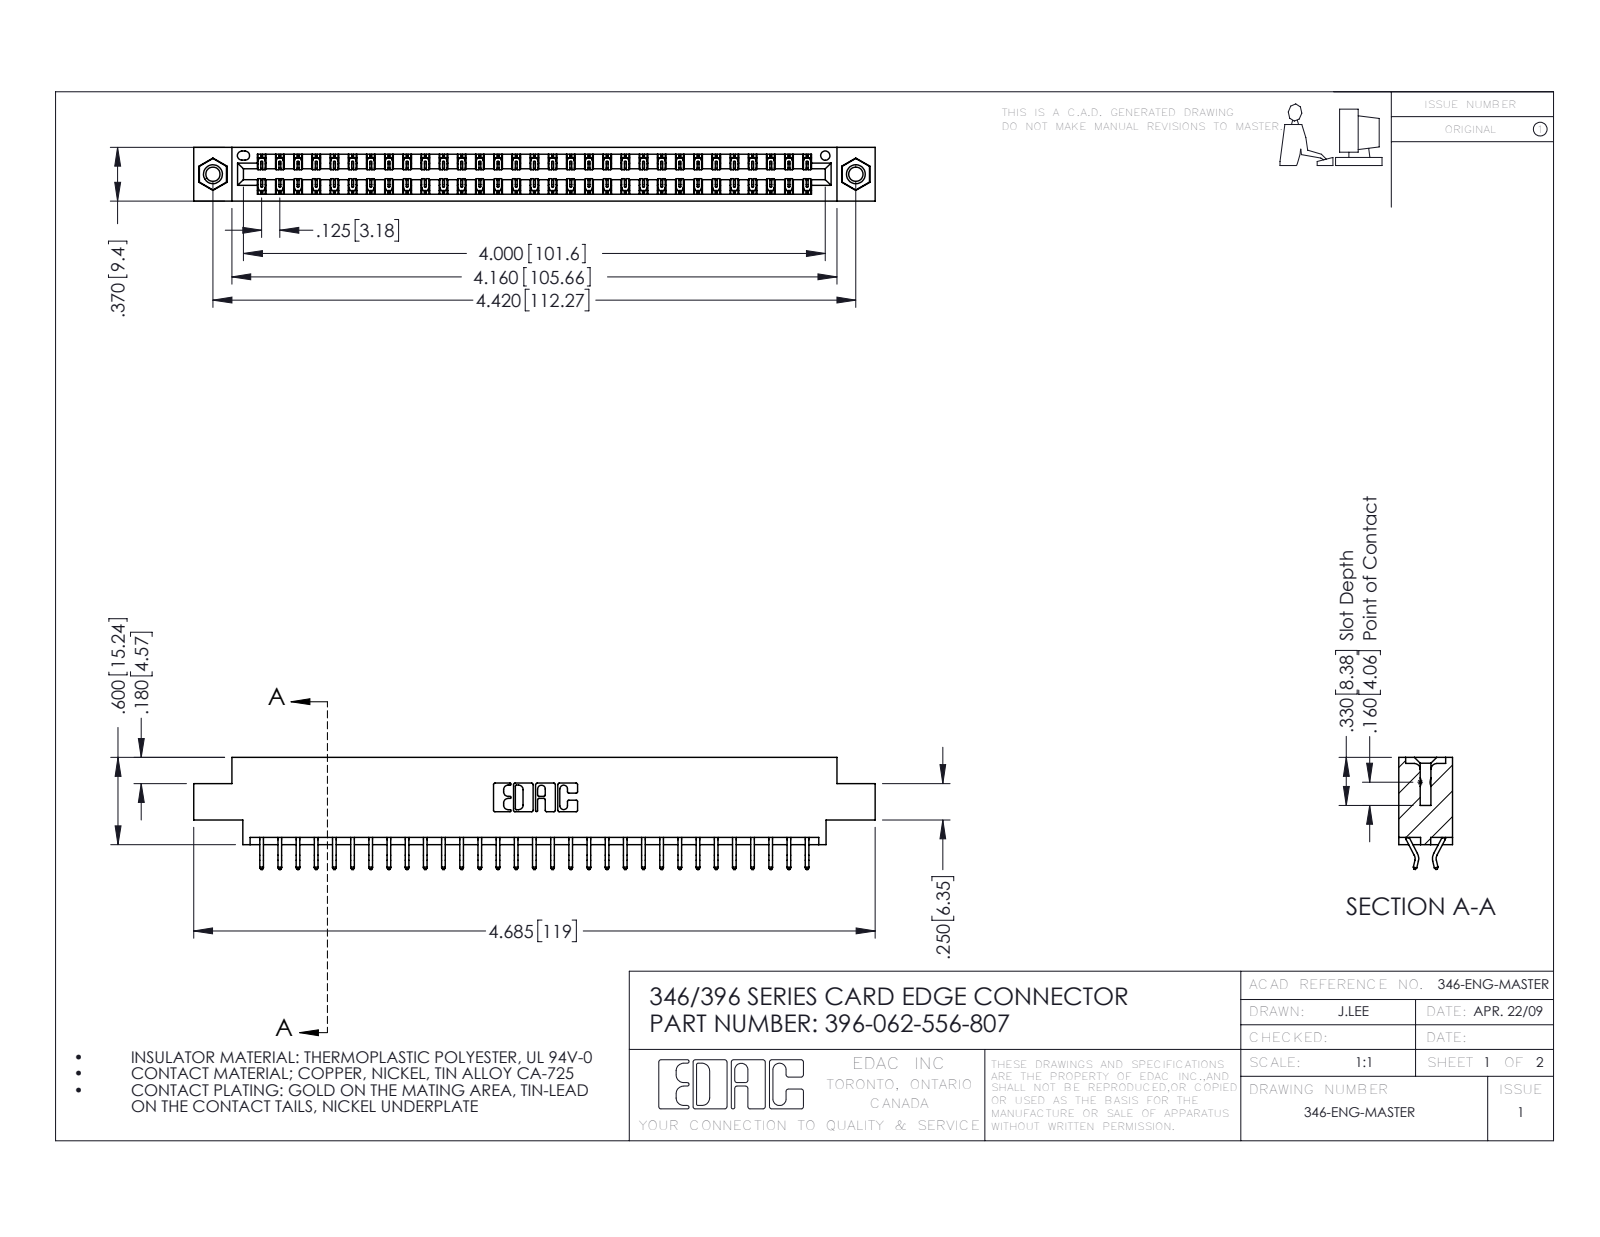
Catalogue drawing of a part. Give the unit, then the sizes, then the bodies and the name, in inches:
Units: inches
Overall size (bounding box): 4.685 × 0.77 × 0.37
Round holes (diameter × count): ⌀0.098 ×2, ⌀0.125 ×2, ⌀0.156 ×2, ⌀0.064 ×1
Round bosses / shafts (diameter × count): ⌀0.155 ×2
Partial cylindrical surfaces — rounded edges, fillets, slot ends (radius × count): R0.006 ×93, R0.01 ×22, R0.007 ×6, R0.031 ×6, R0.026 ×3, R0.01 ×2, R0.014 ×2, R0.022 ×2
Main face-to-face distances: 0.048, 0.322, 0.37, 0.25, 0.025, 0.072, 0.298, 0.275, 0.222, 0.148
Hole centre spacings: 0.246, 4.212, 4.42
Volume: 0.692 in³ · Surface area: 24.15 in²
Bodies: 65 solids, 3782 faces (2530 planar, 1236 cylindrical, 16 other)
Part name (STEP PRODUCT): 396-062-556-807; 345-250-001_345-250-005-103; 346 Part_0.170 Offset - 0.156 Dia-TI; 345-292-001_556 Tail
STEP written by: SolidWorks 2016 (CONFIG_CONTROL_DESIGN)
